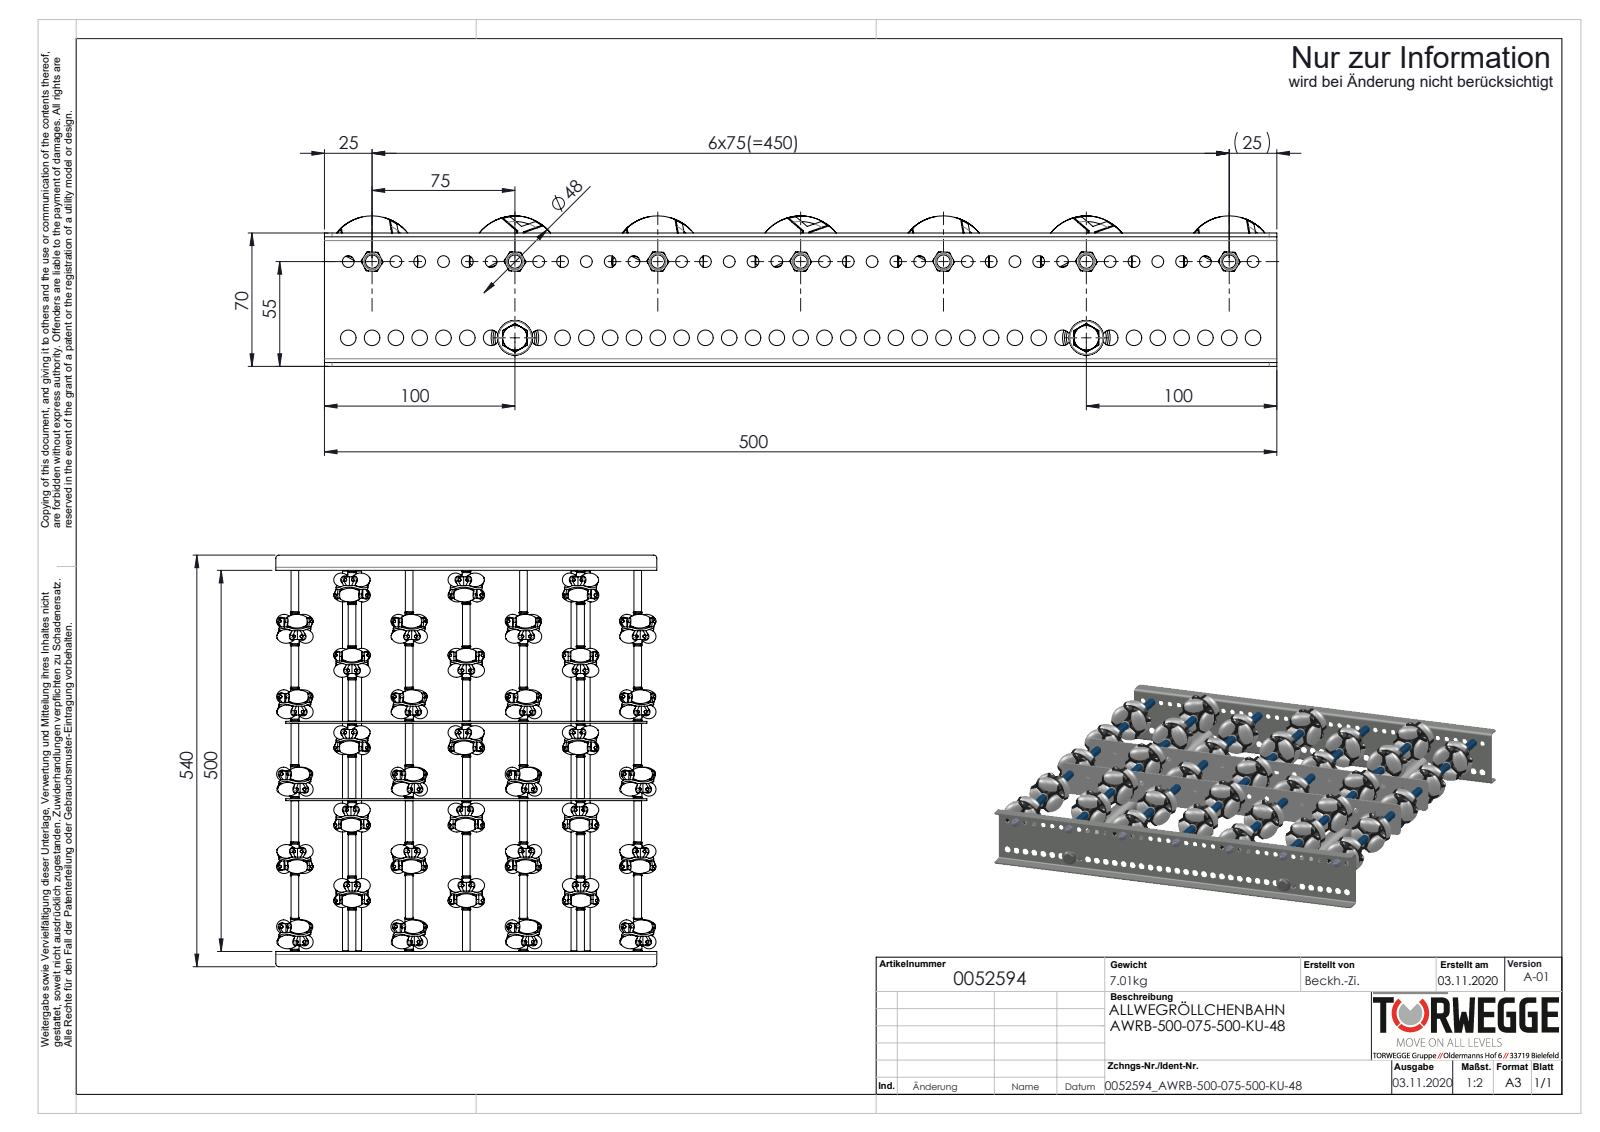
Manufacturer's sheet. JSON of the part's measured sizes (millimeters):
{"part_name": "AWR48_Halter; AWR48_Röllchen; S108767_Längstraverse-42x2,5-AWR_L500; 0019730_Tragrollenrohr-Ø10x1,75KU_KFG_0019730_L=54 (+8 more)", "step_written_by": "SolidWorks 2020 (AUTOMOTIVE_DESIGN)", "units": "millimeters", "bodies": {"solids": 595, "faces": 10670, "planar": 3688, "cylindrical": 4162, "other": 2820}, "overall_size": [540, 500, 79], "volume_mm3": 2142000, "surface_area_mm2": 1504000, "round_holes": [[3.7, 210], [4.2, 210], [6.2, 39], [8.2, 39], [6.5, 19], [4.92, 7], [8.4, 7], [6.8, 2], [21, 2]], "round_bosses_or_shafts": [[4, 210], [3.7, 175], [8, 9], [42, 7], [11, 7], [10, 7], [7, 7], [6, 7]], "partial_cylinders_radius": [[4, 8], [23.55, 7], [2, 4], [5, 4]], "face_to_face_distances": [2, 502, 101.5, 2.5, 68, 500, 504, 3, 99, 104], "hole_center_spacings": [36.06, 36.05, 36.04, 12.5, 25, 37.5, 87.5, 50]}
